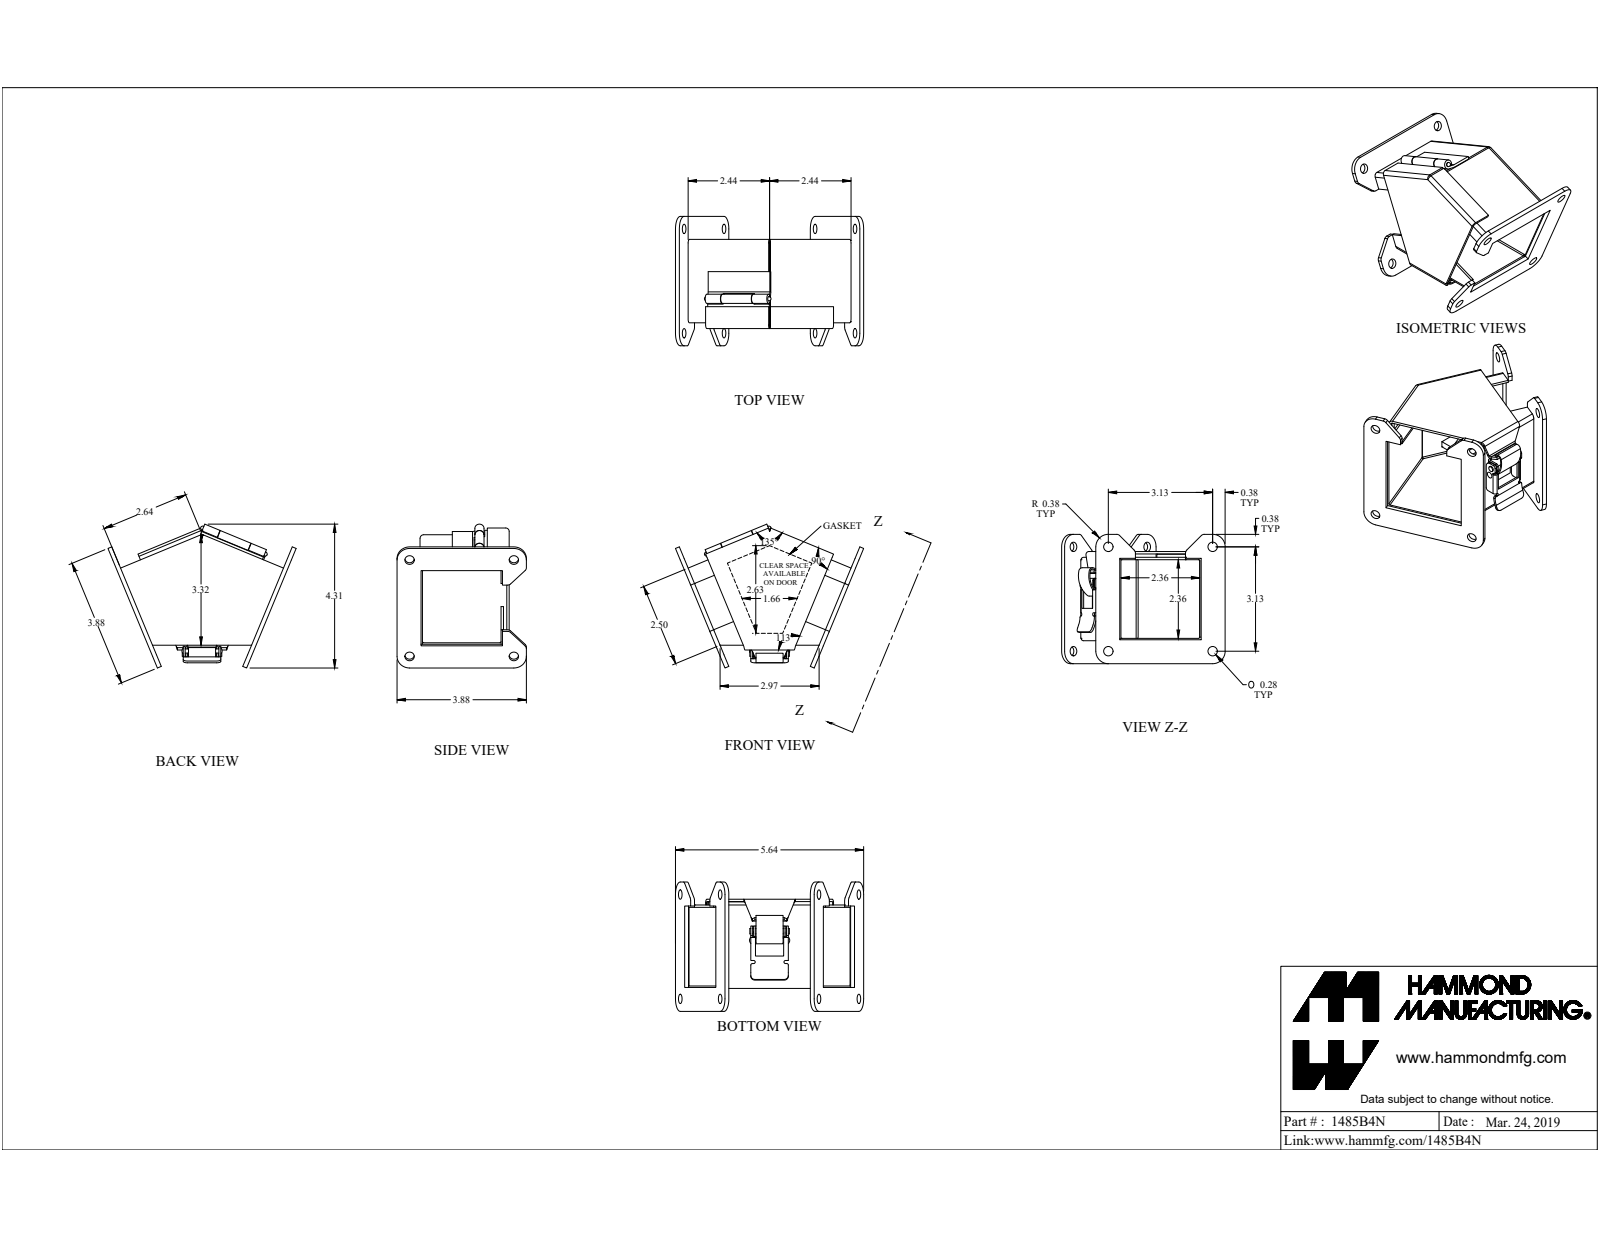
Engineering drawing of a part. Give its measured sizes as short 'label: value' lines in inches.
name: 1485B4N
written by: SolidWorks 2019 (CONFIG_CONTROL_DESIGN)
unit: in
bodies: 10 solids, 265 faces (155 planar, 94 cylindrical, 16 other)
size: 5.639 × 4.309 × 3.875
volume: 5.809 in³; area: 153.7 in²
holes: 8× ⌀0.281, 2× ⌀0.125, 1× ⌀0.164
bosses: 1× ⌀0.275, 1× ⌀0.275, 1× ⌀0.162, 1× ⌀0.158, 1× ⌀0.125, 1× ⌀0.125
rounds: 11× R0.125, 10× R0.036, 10× R0.108, 8× R0.375, 4× R0.029, 4× R0.086, 2× R0.015, 2× R0.047
face distances: 0.072, 2.6, 0.172, 2.428, 2.528, 2.672, 0.125, 0.125, 0.187, 0.1
hole spacings: 3.125, 3.125, 4.419, 1.041, 2.097, 3.163, 3.163, 3.65
